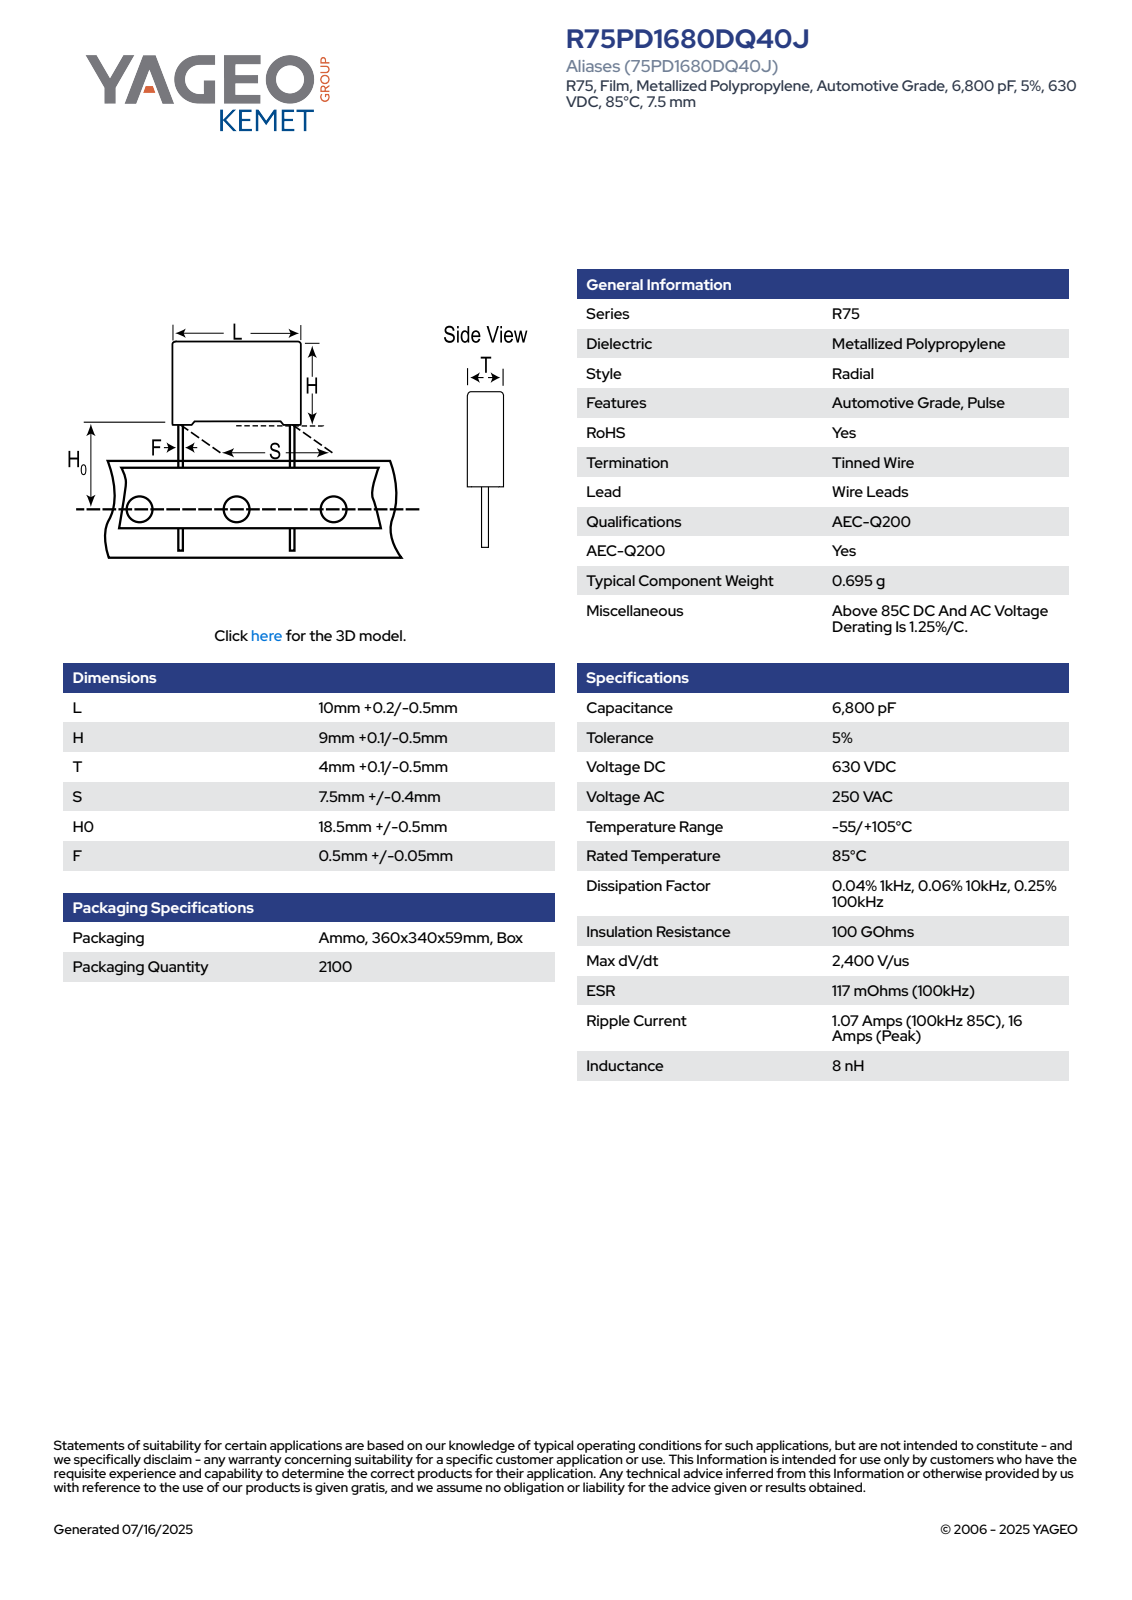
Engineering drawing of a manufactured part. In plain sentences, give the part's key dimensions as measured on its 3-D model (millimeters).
The part is named "CFR_RB2_10X9X4_L10.2H9.1T4.1S7.5H019F0.55". Its 3-D file was written by "SolidWorks 2020 (AUTOMOTIVE_DESIGN)". It is 4 solids with 85 faces: 77 planar, 8 cylindrical and 0 other. Overall it measures 28.1 by 10.2 by 4.11 millimeters. Its volume is 363 cubic millimeters and its surface area 428 square millimeters. Round bosses or shafts: 2 of diameter 0.55. Partial cylindrical surfaces (rounded edges, fillets, slot ends): 4 of radius 0.5. The main face-to-face distances are 4.1, 10.2, 8.35, 0.34, 3.76, 0.75, 9.1, 3.42, 9.86, 0.31.
